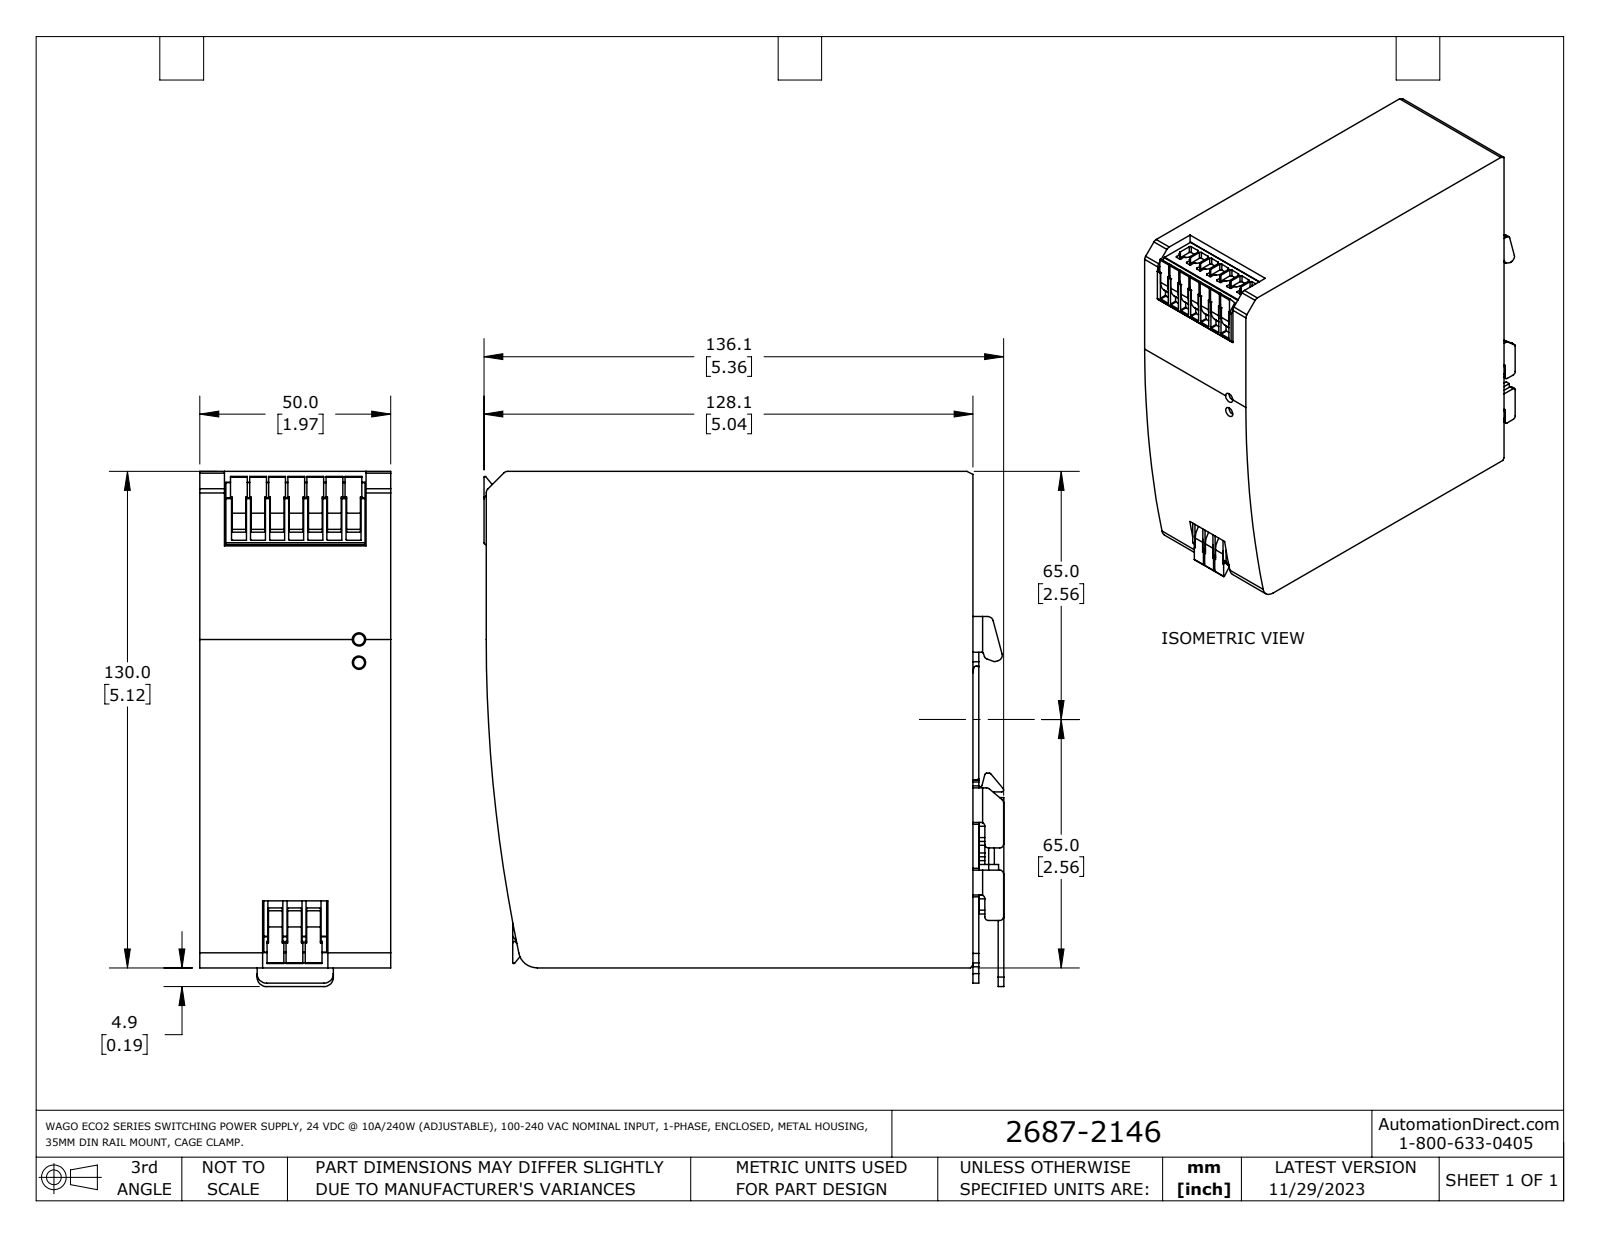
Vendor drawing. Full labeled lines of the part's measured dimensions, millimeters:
Part name (STEP PRODUCT): 2687-2146
STEP written by: SolidWorks 2023 (AUTOMOTIVE_DESIGN)
Units: millimetres
Bodies: 1 solid, 719 faces (421 planar, 298 cylindrical, 0 other)
Overall size (bounding box): 136.2 × 134.9 × 50
Volume: 820 000 mm³ · Surface area: 69 810 mm²
Round holes (diameter × count): ⌀3.5 ×2
Round bosses / shafts (diameter × count): ⌀2.9 ×2
Partial cylindrical surfaces — rounded edges, fillets, slot ends (radius × count): R0.5 ×67, R1 ×40, R0.3 ×26, R0.2 ×20, R2.5 ×16, R0.2 ×12, R0.8 ×6, R0.7 ×4
Main face-to-face distances: 50, 130, 1.5, 6.6, 127.5, 129, 2.5, 134.1, 5.1, 135.6
Hole centre spacings: 6.1
